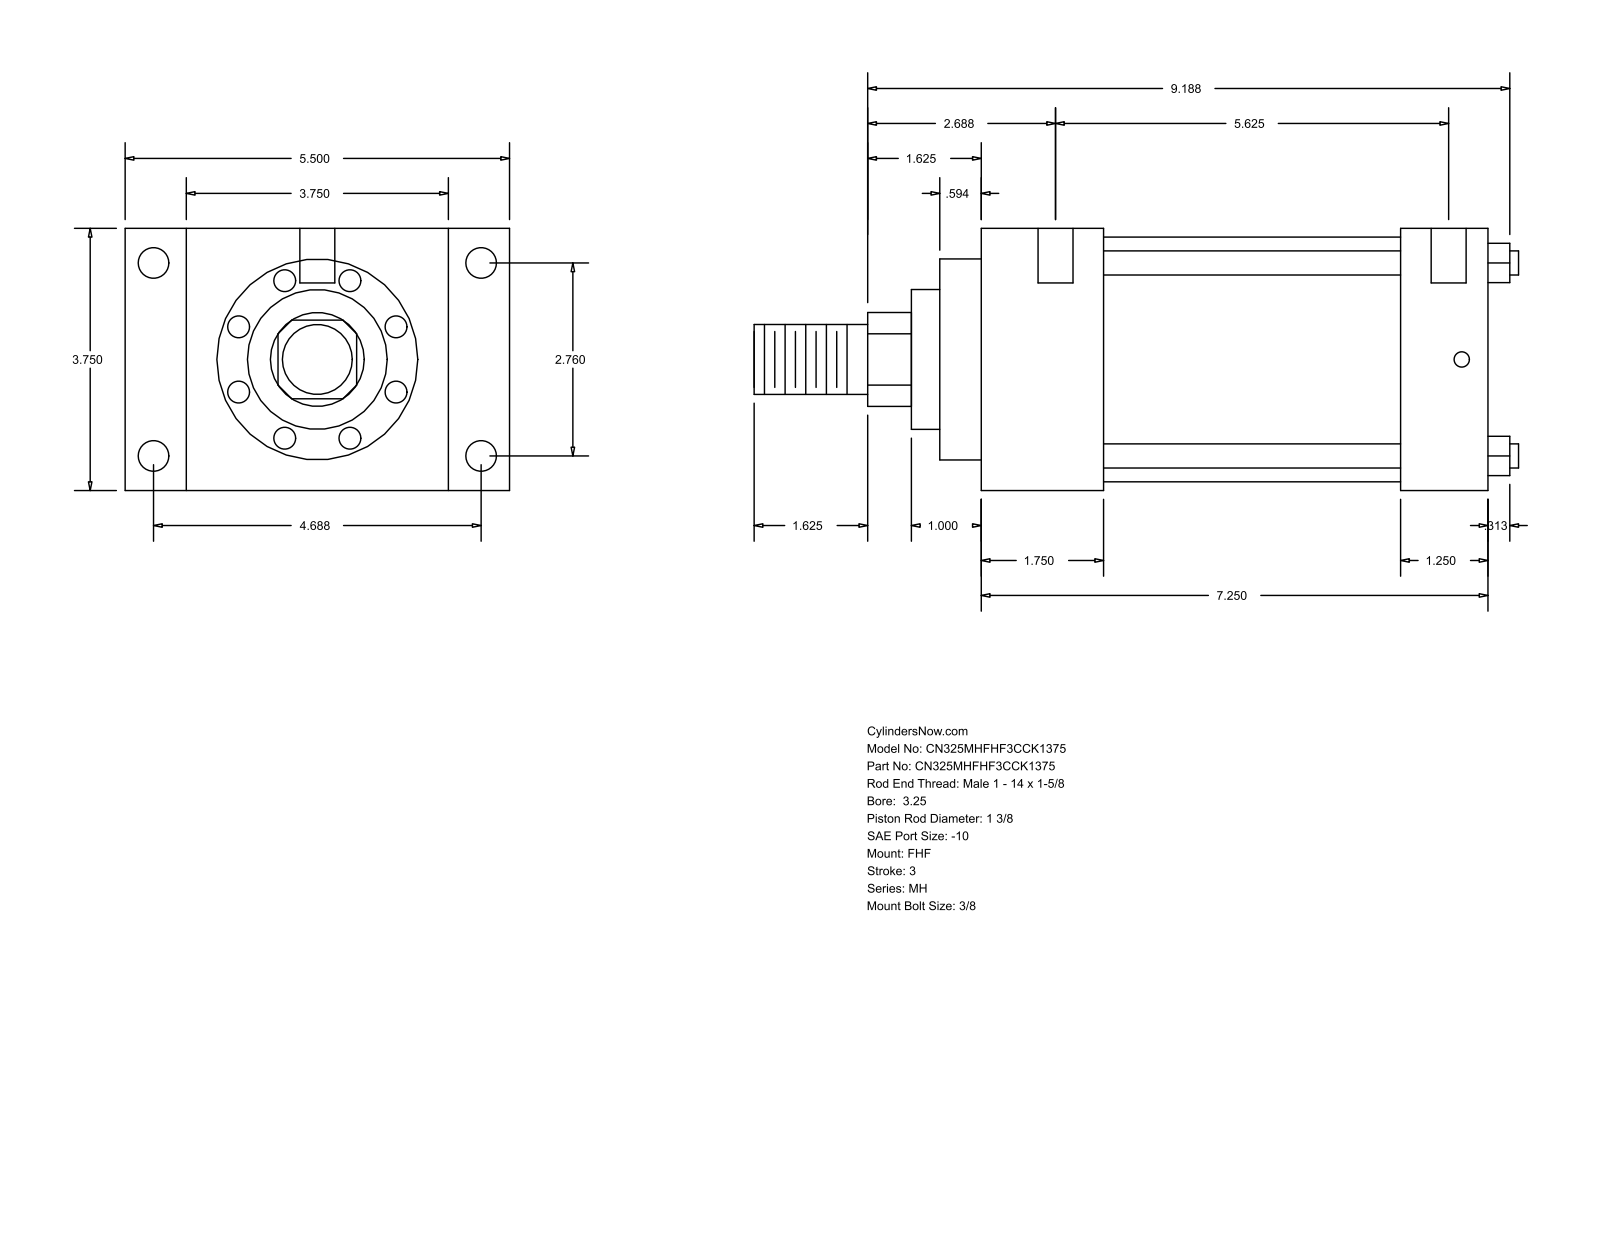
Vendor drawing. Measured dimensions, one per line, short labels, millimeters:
name: MH_FHF__0325_1.375
written by: GSSL Pune (CONFIG_CONTROL_DESIGN)
unit: mm
bodies: 0 solids, 90 faces (61 planar, 29 cylindrical, 0 other)
size: 277.81 × 139.7 × 95.25
holes: 4× ⌀5.56, 4× ⌀11.13, 2× ⌀12.7
bosses: 4× ⌀8.76, 1× ⌀88.9, 1× ⌀73.03, 1× ⌀50.8, 1× ⌀34.92, 1× ⌀25.4
rounds: 1× R17.06
face distances: 95.24, 184.16, 44.45, 139.71, 22.23, 117.47, 139.7, 152.41, 107.96, 31.75
hole spacings: 70.1, 119.06, 138.16, 149.23, 1.59, 4.76, 142.88, 144.47
